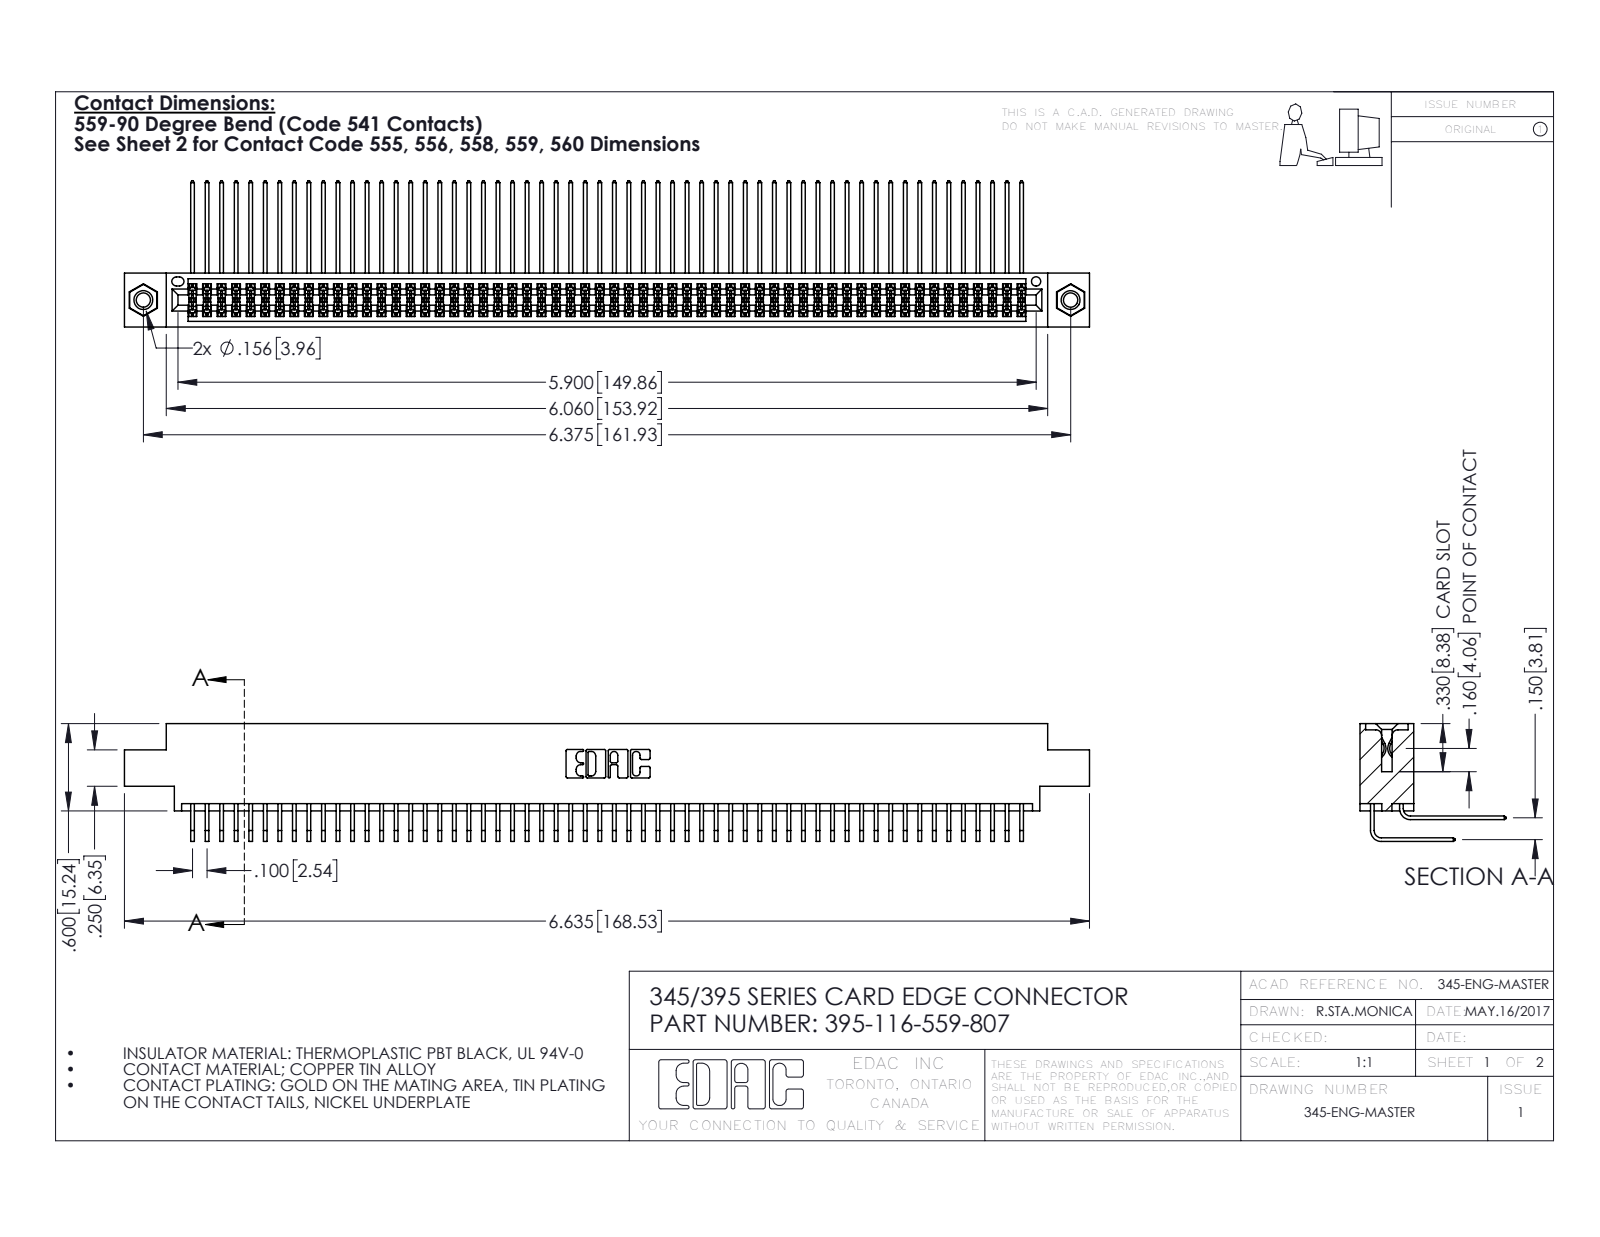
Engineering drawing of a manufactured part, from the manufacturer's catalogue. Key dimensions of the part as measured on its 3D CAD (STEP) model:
Part name (STEP PRODUCT): 345-292-001_558 559 Tail - 1; 345-250-001_345-250-005-103; 345-292-001_559 Tail - 2; 395-116-559-807 (+1 more)
STEP written by: SolidWorks 2016 (CONFIG_CONTROL_DESIGN)
Units: inches
Bodies: 119 solids, 6222 faces (4176 planar, 2030 cylindrical, 16 other)
Overall size (bounding box): 6.635 × 1.005 × 0.809
Volume: 1.041 in³ · Surface area: 44.71 in²
Round holes (diameter × count): ⌀0.098 ×2, ⌀0.125 ×2, ⌀0.156 ×2, ⌀0.064 ×1
Round bosses / shafts (diameter × count): ⌀0.155 ×2
Partial cylindrical surfaces — rounded edges, fillets, slot ends (radius × count): R0.006 ×175, R0.01 ×22, R0.007 ×6, R0.031 ×6, R0.026 ×3, R0.014 ×2, R0.019 ×2, R0.022 ×2
Main face-to-face distances: 0.072, 0.298, 0.37, 0.2, 0.098, 0.272, 0.025, 0.225, 0.175, 0.15
Hole centre spacings: 0.27, 6.139, 6.375
